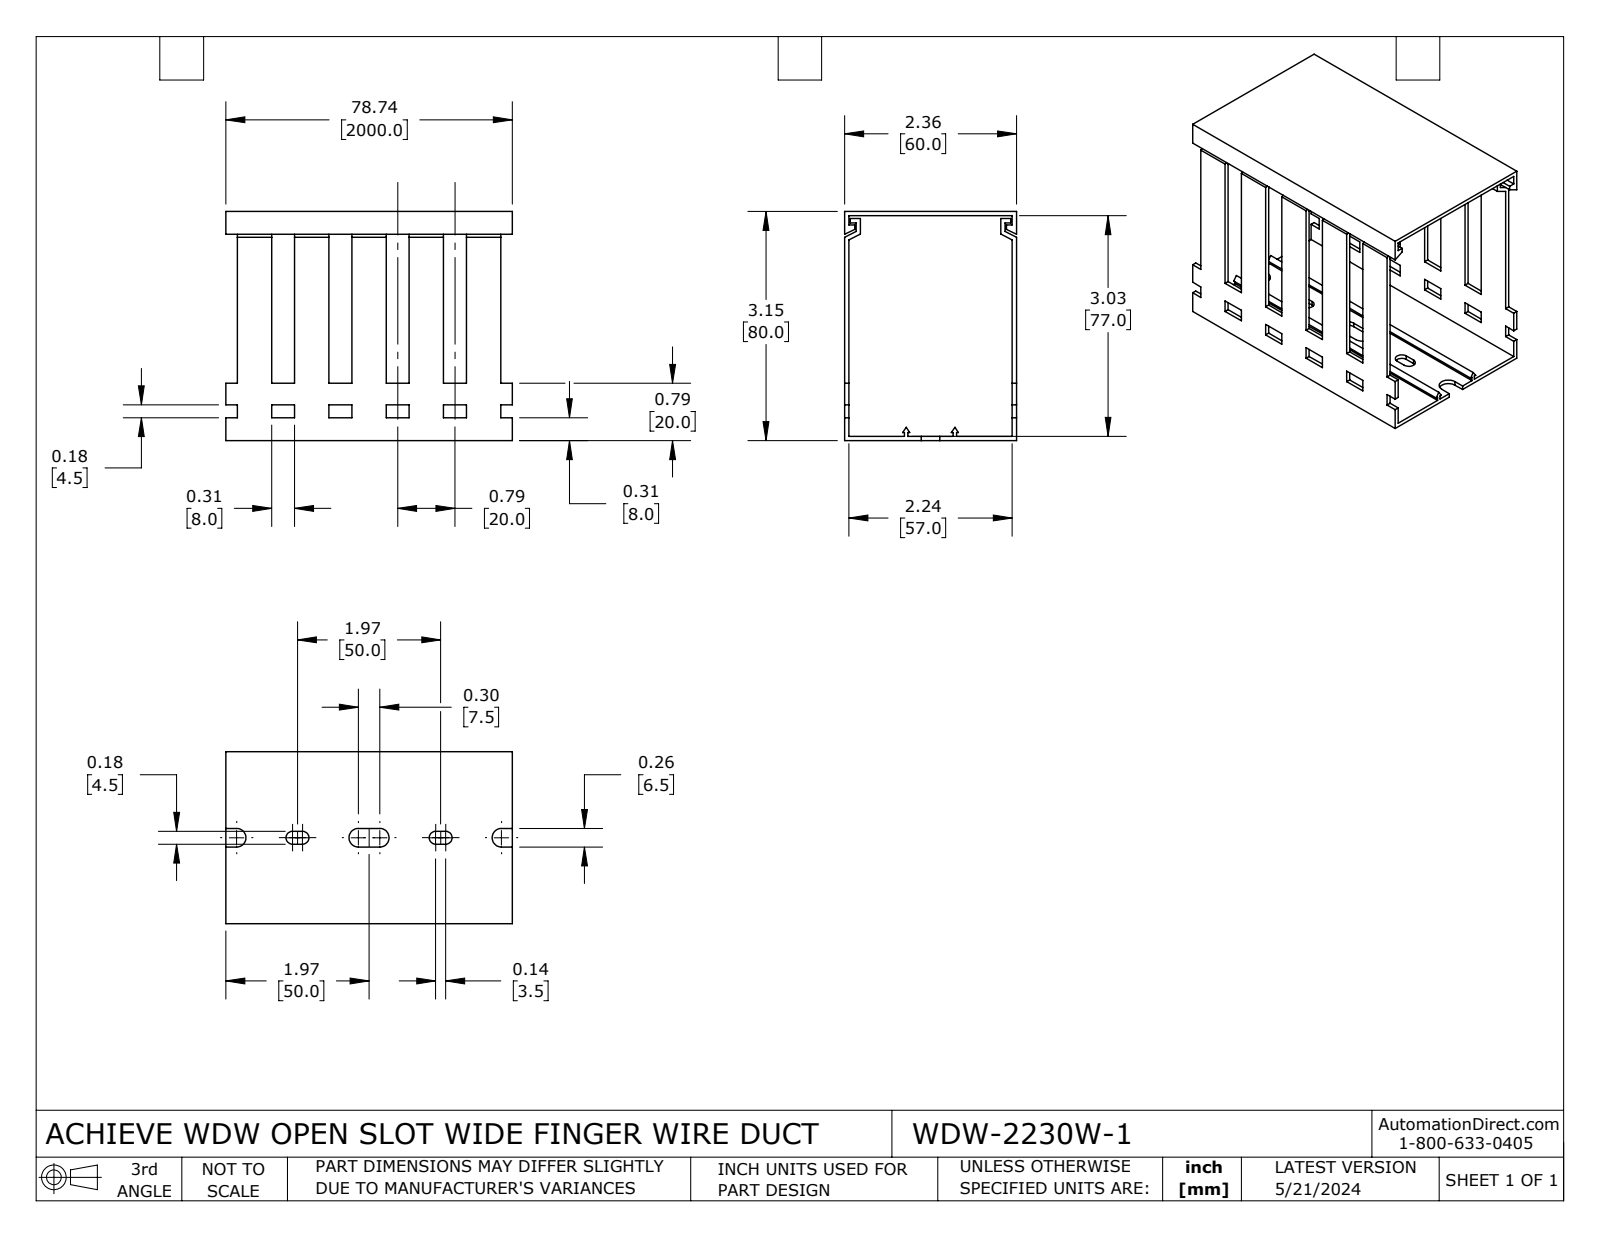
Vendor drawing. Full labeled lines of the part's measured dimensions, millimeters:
Part name (STEP PRODUCT): WDW-2230W-1
STEP written by: SolidWorks 2023 (CONFIG_CONTROL_DESIGN)
Units: millimetres
Bodies: 2 solids, 210 faces (198 planar, 12 cylindrical, 0 other)
Overall size (bounding box): 100 × 80 × 60
Volume: 37 233 mm³ · Surface area: 53 159 mm²
Partial cylindrical surfaces — rounded edges, fillets, slot ends (radius × count): R2.25 ×4, R3.25 ×4
Main face-to-face distances: 1.5, 78.5, 58.5, 60, 80, 77, 57, 20, 4, 40
